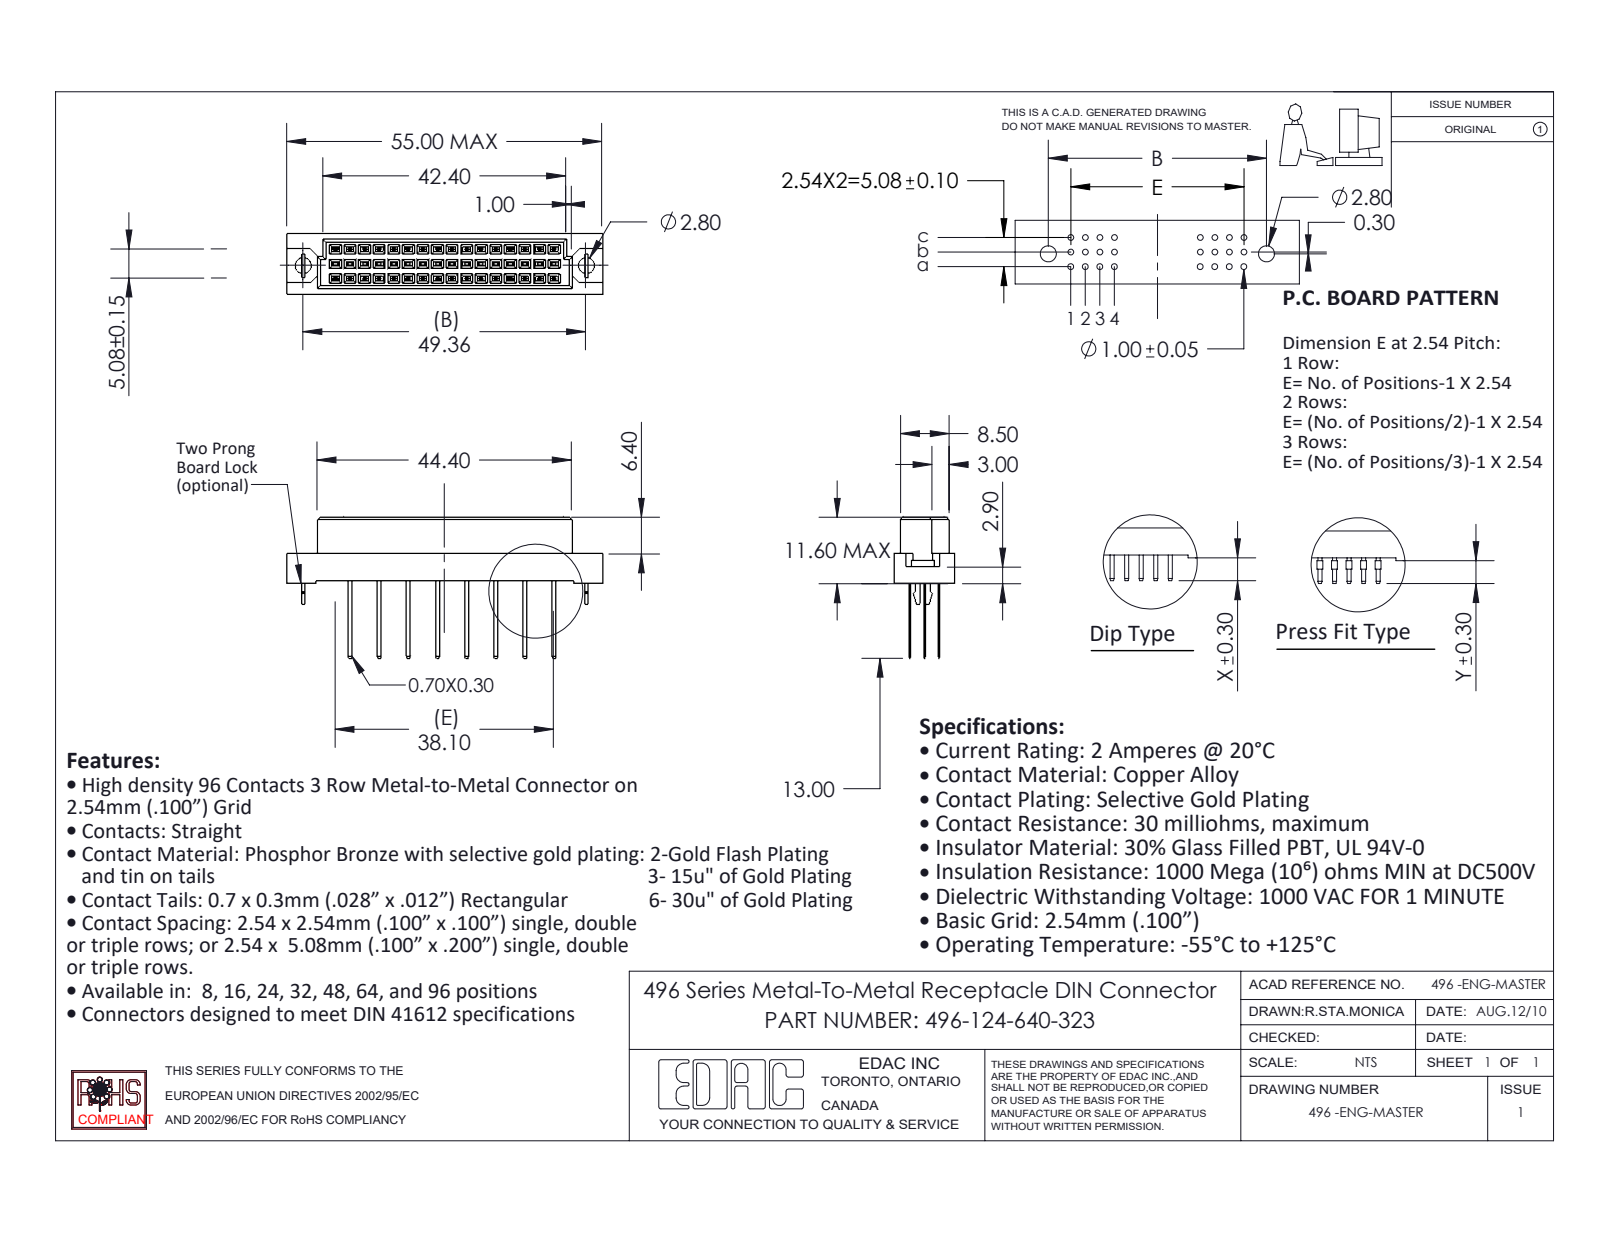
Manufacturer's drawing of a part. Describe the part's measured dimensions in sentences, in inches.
The part is named "496-124-640-323; 496-290_40; 496 Bore-lock; 496 Part_48". Its 3-D file was written by "SolidWorks 2020 (CONFIG_CONTROL_DESIGN)". It is 27 solids with 942 faces: 936 planar, 6 cylindrical and 0 other. Overall it measures 2.165 by 0.969 by 0.417 inches. Its volume is 0.287 cubic inches and its surface area 8.004 square inches. Round holes: 2 of diameter 0.11. Partial cylindrical surfaces (rounded edges, fillets, slot ends): 1 of radius 0.021. The main face-to-face distances are 0.1, 0.2, 0.041, 0.376, 0.022, 0.022, 0.032, 0.112, 0.061, 0.073. The hole center spacings are 1.943.
